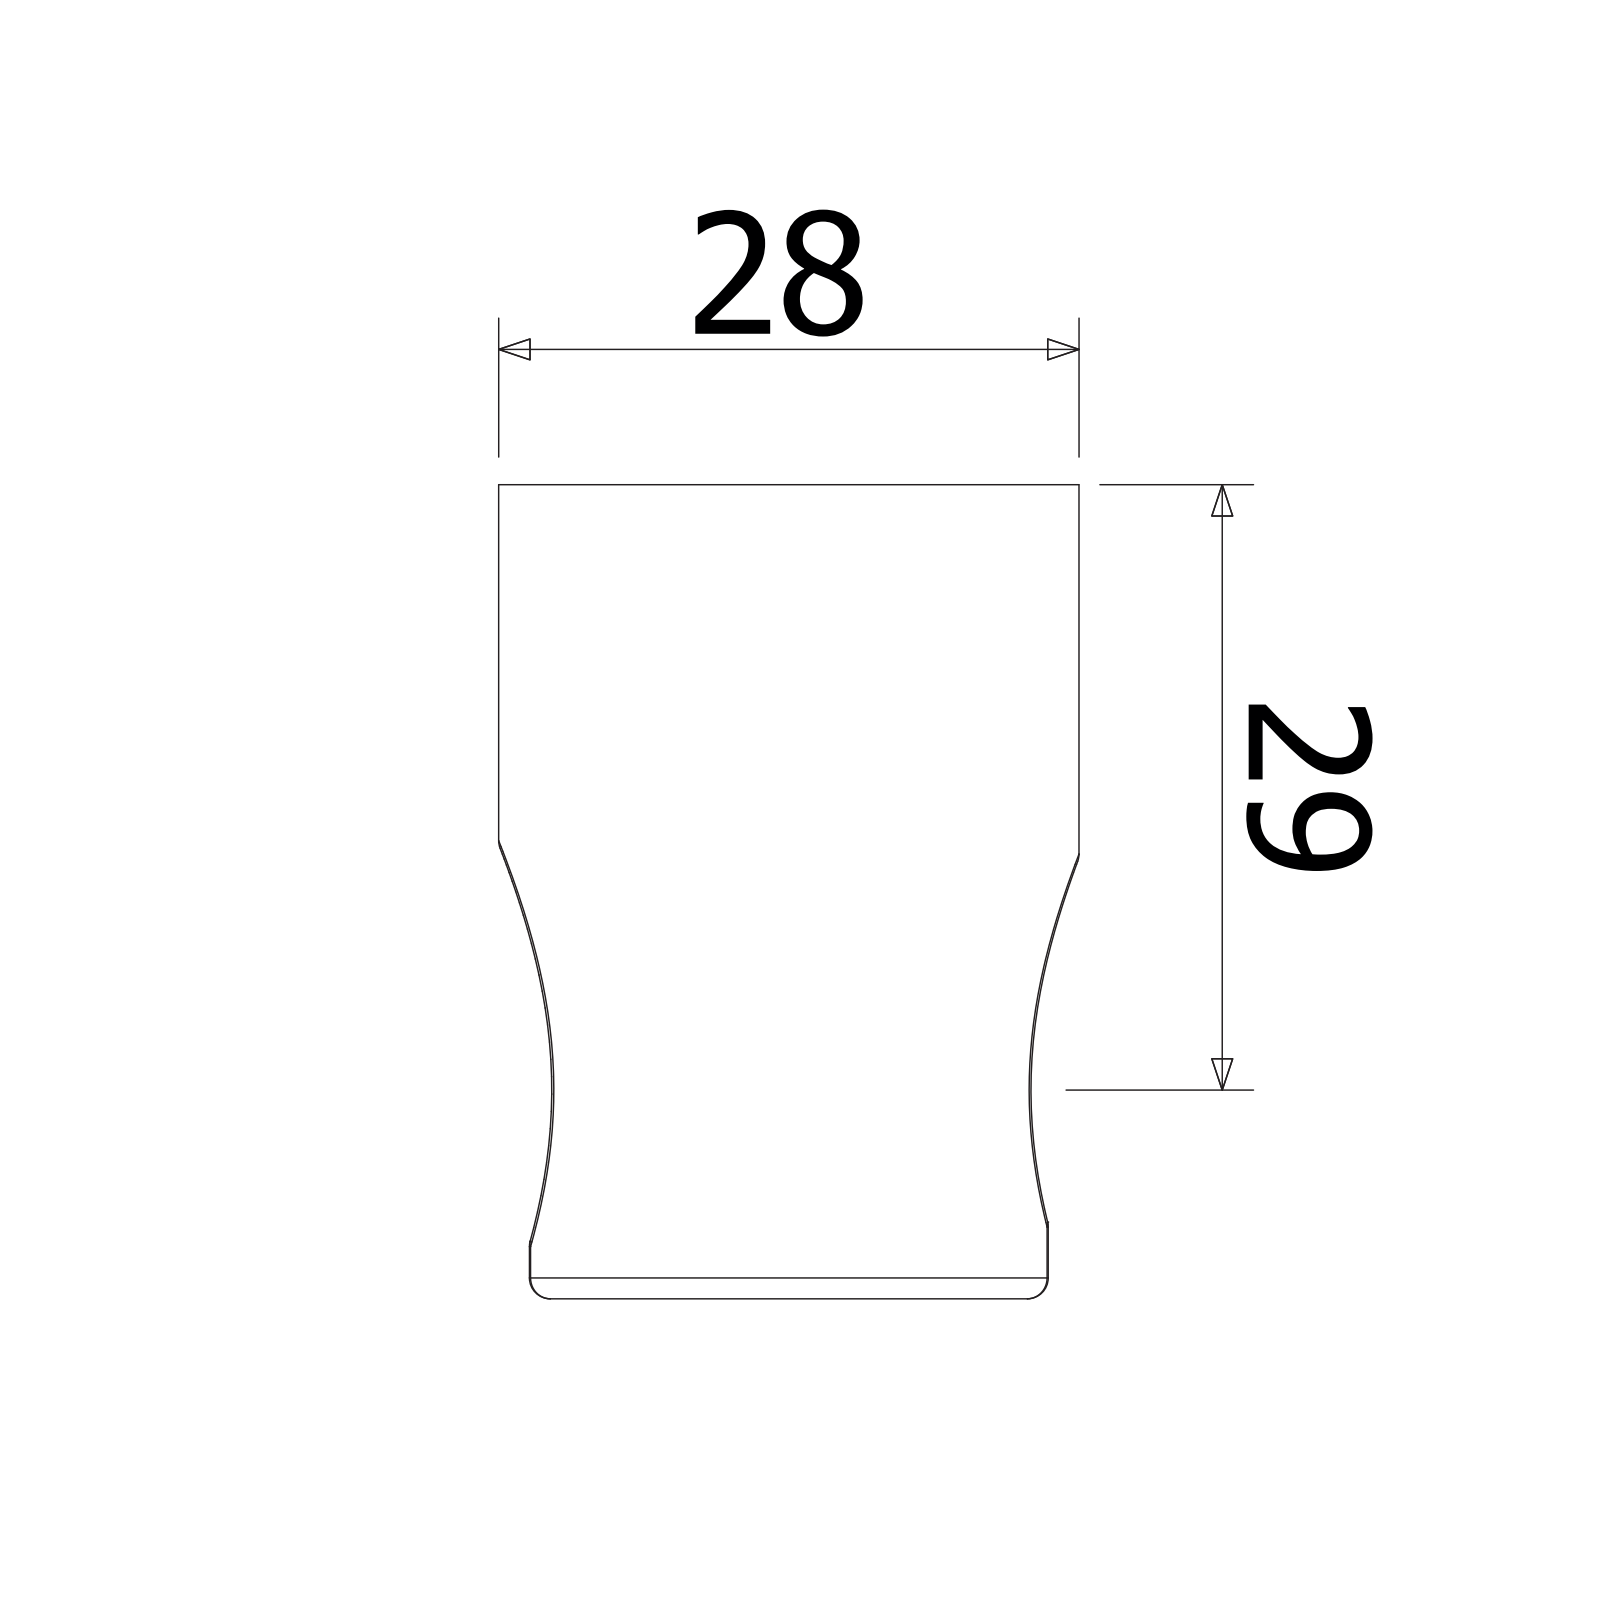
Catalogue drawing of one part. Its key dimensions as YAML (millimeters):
part_name: "ZSUP030CR"
step_written_by: "CREO PARAMETRIC BY PTC INC, 2020044 (CONFIG_CONTROL_DESIGN)"
units: millimeters
bodies: {solids: 1, faces: 40, planar: 7, cylindrical: 14, other: 19}
overall_size: [42, 39, 27.8]
volume: 25119
surface_area: 6753
round_holes:
  - {diameter: 4, count: 2}
  - {diameter: 7.5, count: 2}
partial_cylinders:
  - {radius: 1, count: 6}
face_to_face_distances: [39, 13.3, 25.7, 16.5]
hole_center_spacings: [12]
